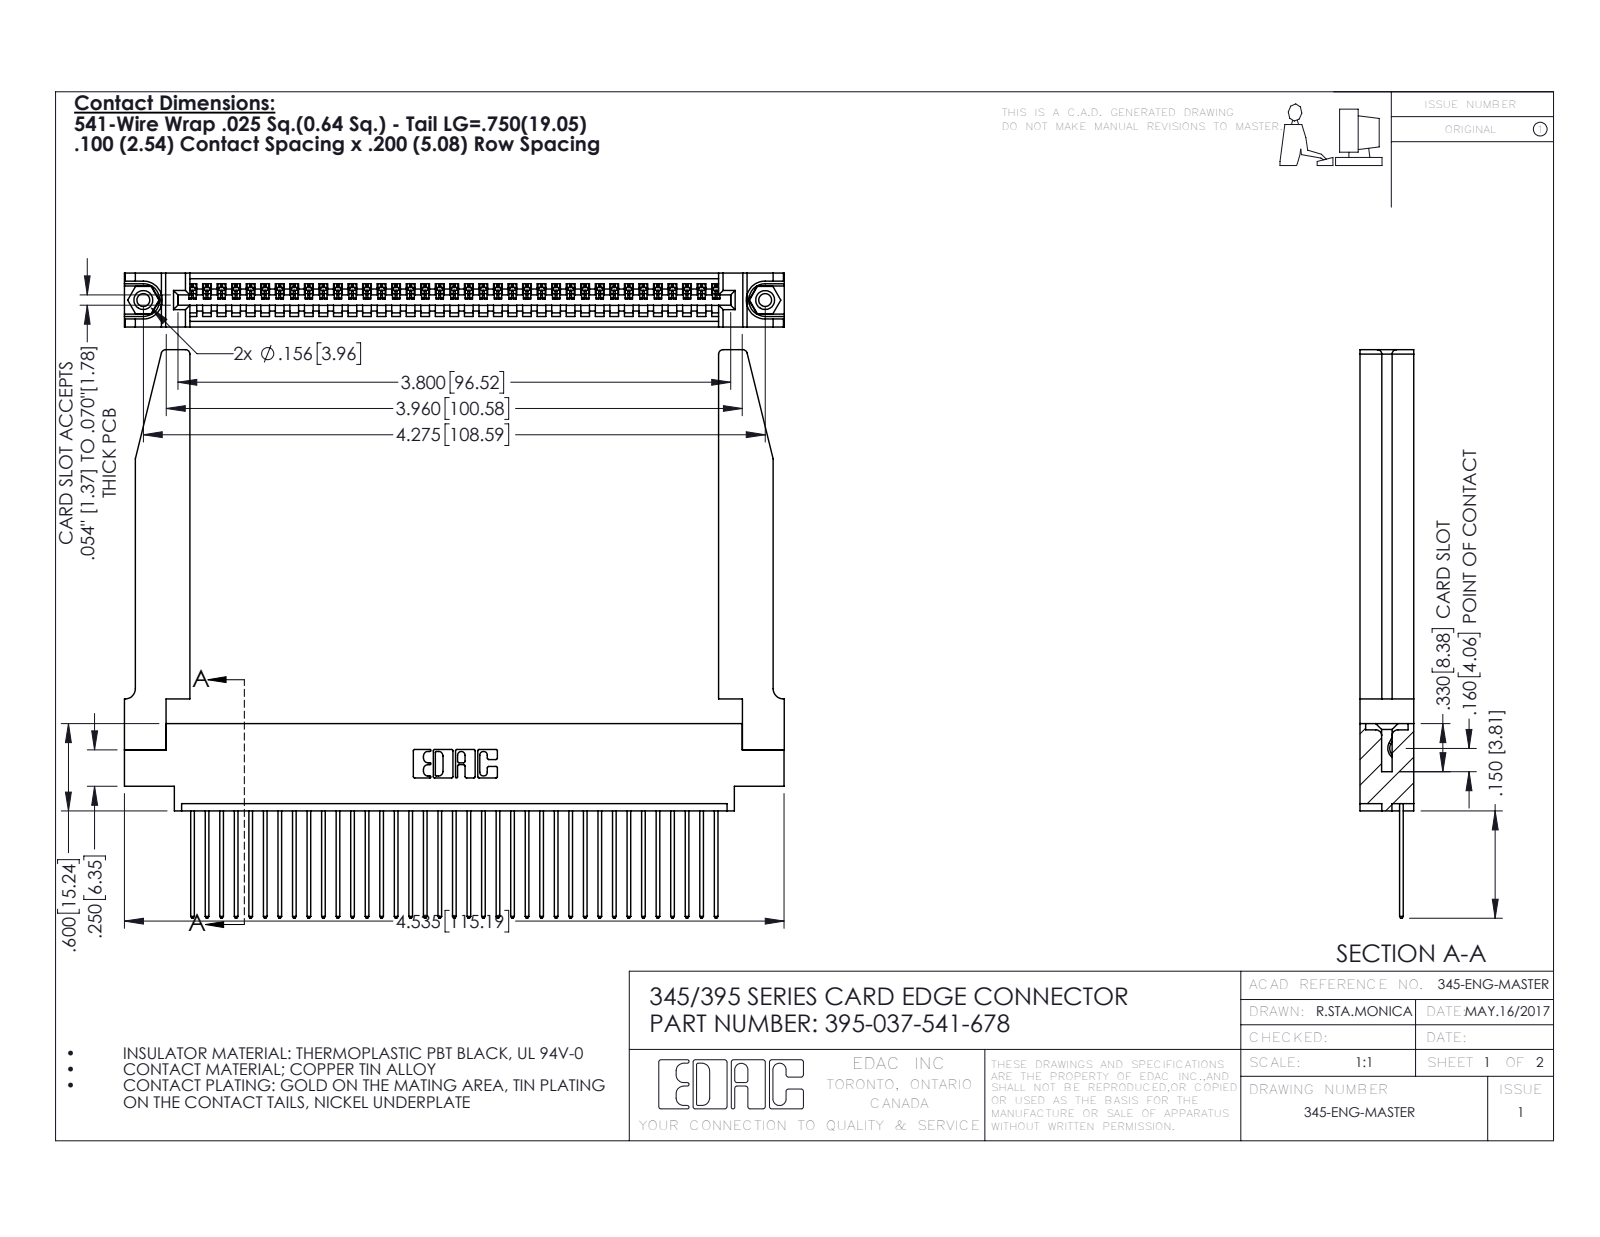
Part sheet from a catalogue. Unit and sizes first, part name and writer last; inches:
Units: inches
Overall size (bounding box): 4.536 × 3.907 × 0.37
Round holes (diameter × count): ⌀0.089 ×2, ⌀0.125 ×2, ⌀0.156 ×2, ⌀0.064 ×1
Round bosses / shafts (diameter × count): ⌀0.155 ×2
Partial cylindrical surfaces — rounded edges, fillets, slot ends (radius × count): R0.006 ×74, R0.01 ×74, R0.01 ×22, R0.03 ×8, R0.007 ×6, R0.031 ×6, R0.026 ×3, R0.031 ×2
Main face-to-face distances: 0.37, 0.072, 0.298, 0.098, 0.272, 0.025, 0.2, 0.225, 0.15, 0.148
Hole centre spacings: 0.27, 4.039, 4.275
Volume: 1.14 in³ · Surface area: 34.29 in²
Bodies: 42 solids, 2510 faces (1706 planar, 752 cylindrical, 52 other)
Part name (STEP PRODUCT): 345-292-001_345-293-141; 345-250-001_345-250-001-102; 345 Part_0.170 Offset - 0.156 Dia-TH; 345-220-078_345-220-078 (+1 more)
STEP written by: SolidWorks 2016 (CONFIG_CONTROL_DESIGN)
